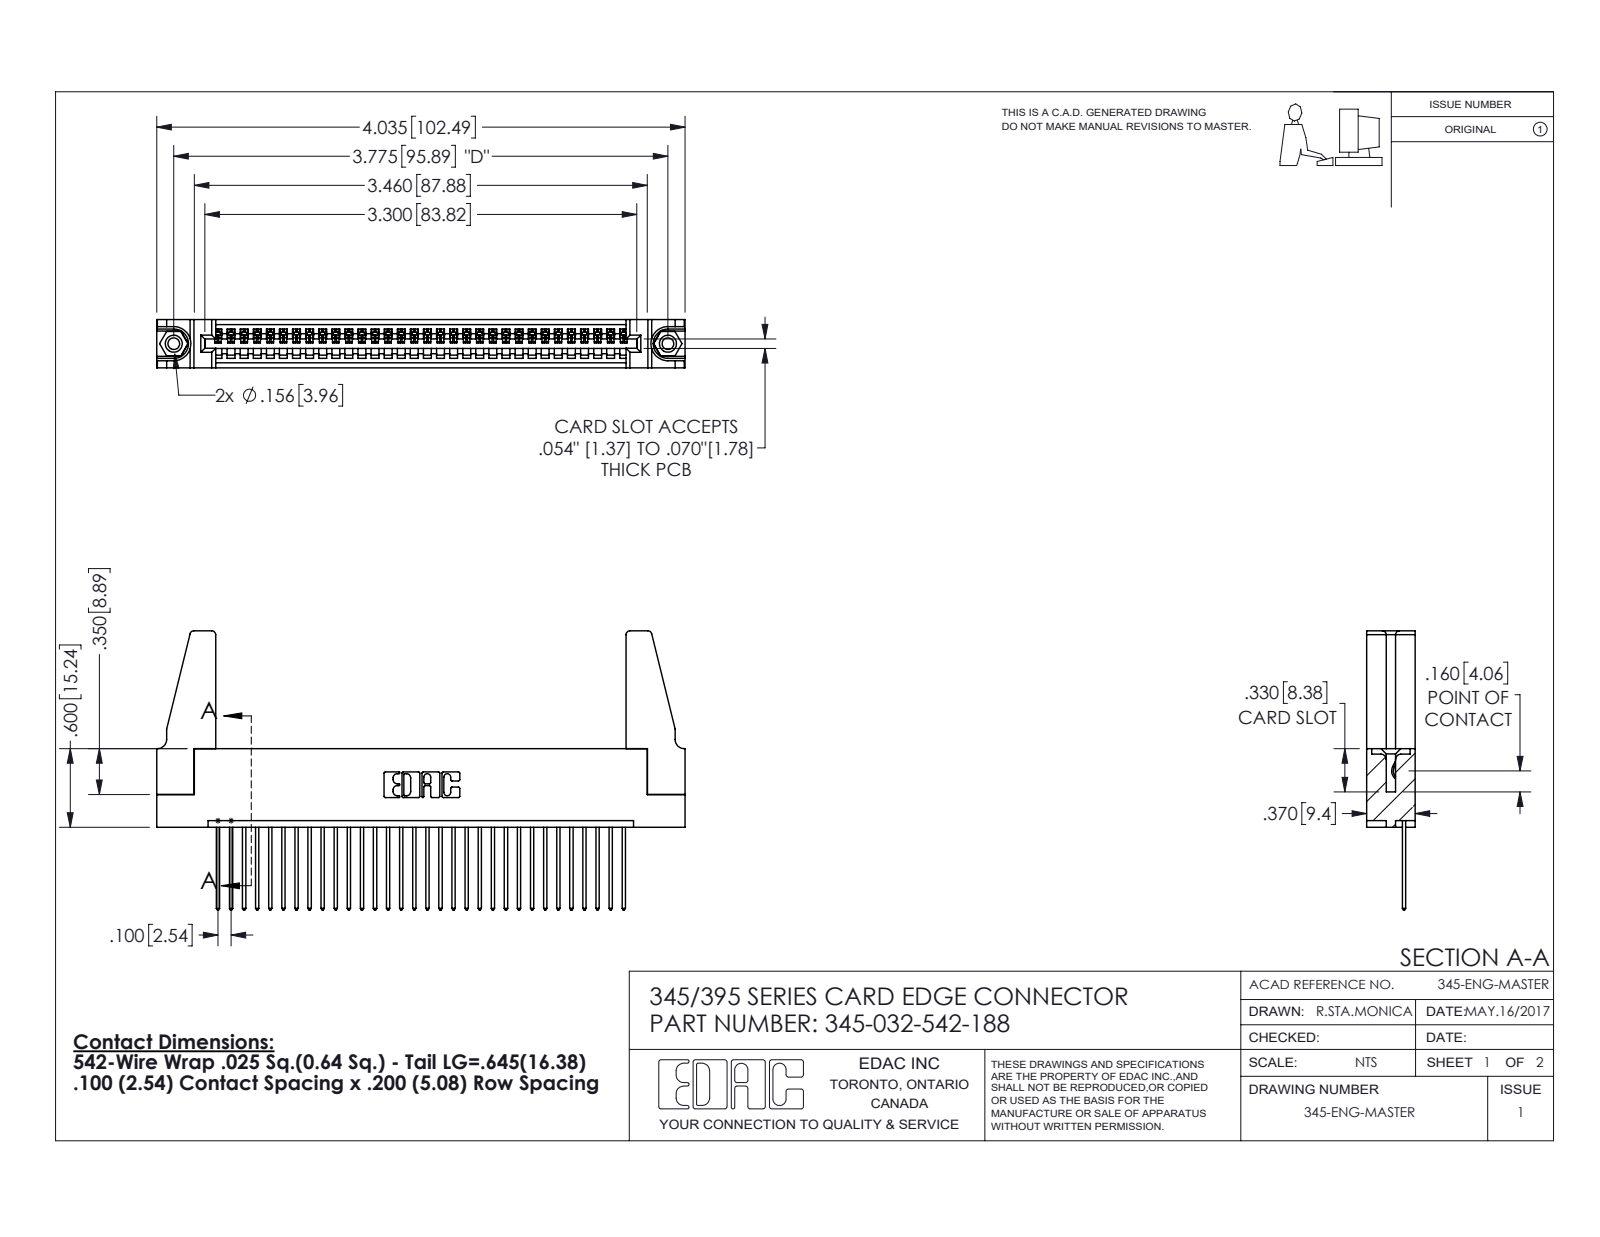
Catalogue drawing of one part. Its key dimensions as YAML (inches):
part_name: "345 Part_Flush Mounting Lugs - 0.156 Dia-TH; 345-250-001_345-250-001-102; 345-292-001_345-293-142; 345-220-078_345-220-088 (+1 more)"
step_written_by: "SolidWorks 2016 (CONFIG_CONTROL_DESIGN)"
units: inches
bodies: {solids: 37, faces: 2106, planar: 1432, cylindrical: 658, other: 16}
overall_size: [4.036, 2.132, 0.37]
volume: 0.792
surface_area: 25.37
round_holes:
  - {diameter: 0.089, count: 2}
  - {diameter: 0.125, count: 2}
  - {diameter: 0.156, count: 2}
  - {diameter: 0.064, count: 1}
round_bosses_or_shafts:
  - {diameter: 0.155, count: 2}
partial_cylinders:
  - {radius: 0.006, count: 64}
  - {radius: 0.01, count: 64}
  - {radius: 0.01, count: 22}
  - {radius: 0.03, count: 8}
  - {radius: 0.007, count: 6}
  - {radius: 0.031, count: 6}
  - {radius: 0.026, count: 3}
  - {radius: 0.031, count: 2}
face_to_face_distances: [0.072, 0.298, 0.37, 0.2, 0.098, 0.272, 0.025, 0.225, 0.149, 0.072]
hole_center_spacings: [0.27, 3.54, 3.775]
